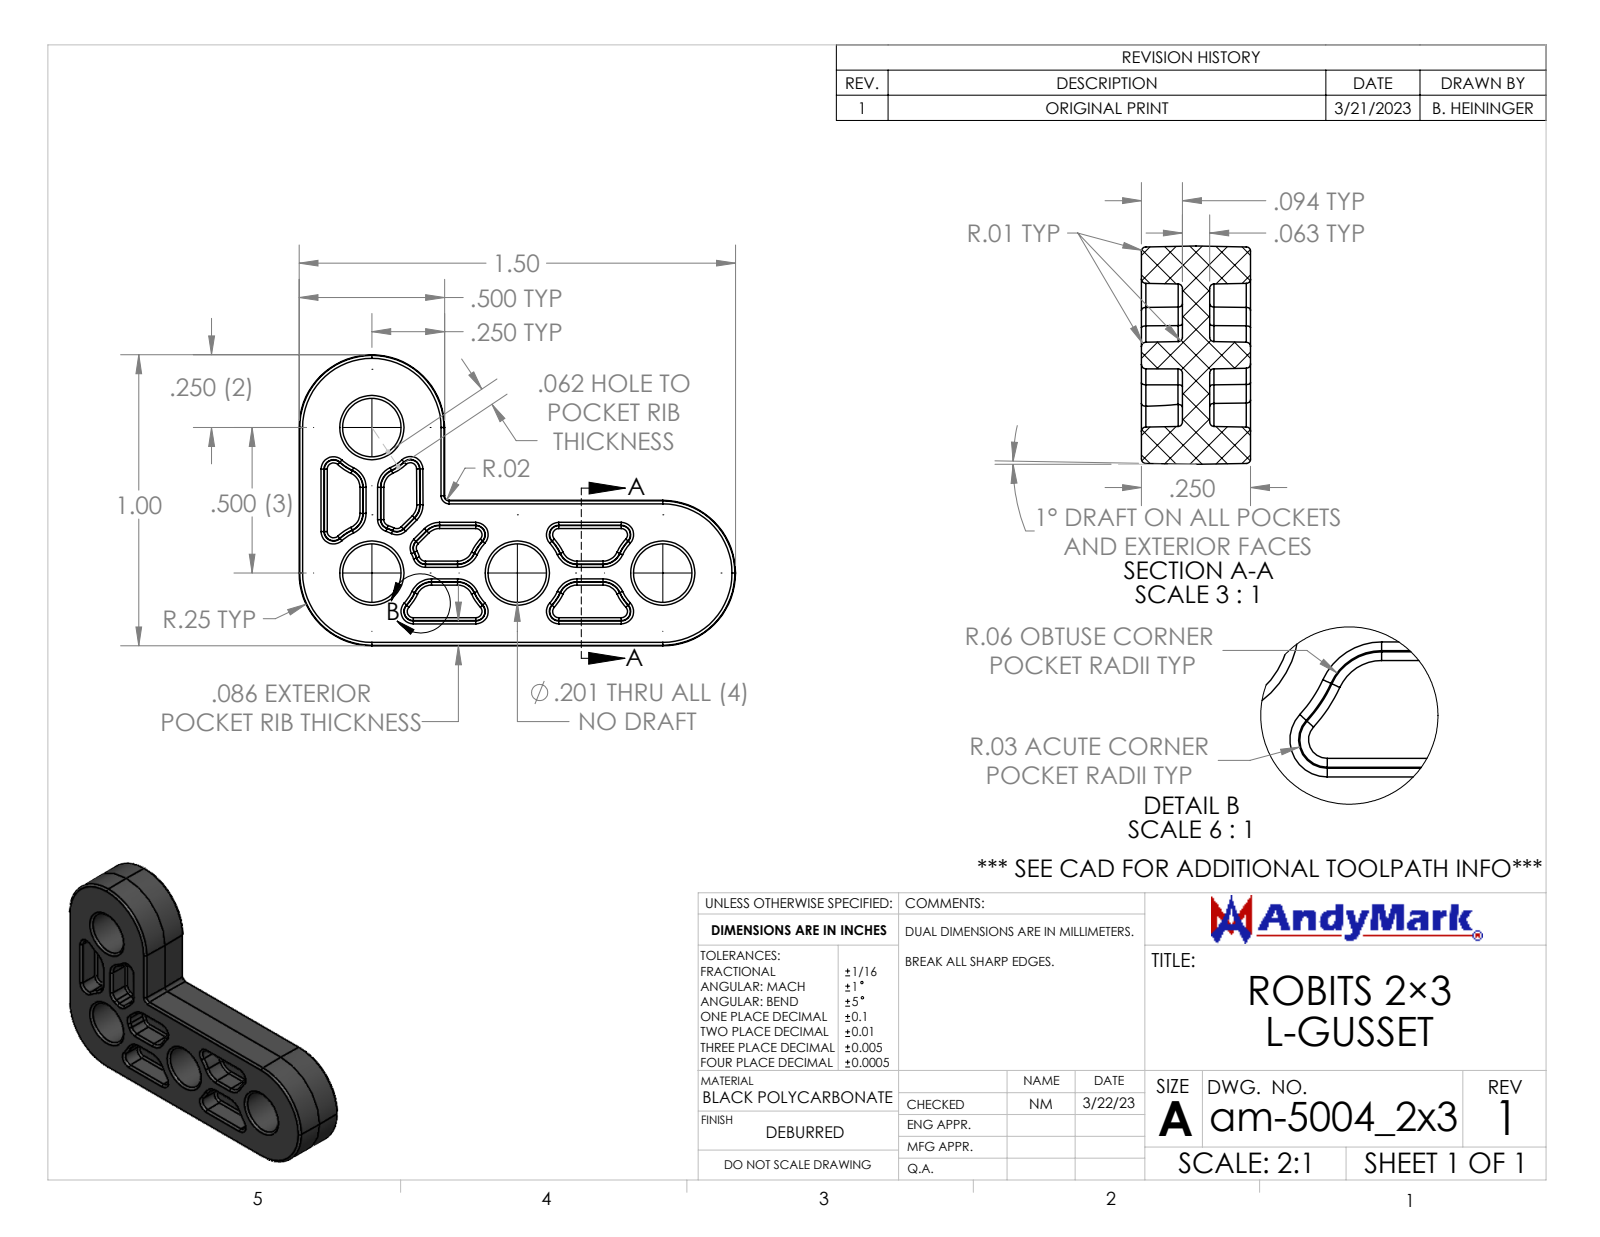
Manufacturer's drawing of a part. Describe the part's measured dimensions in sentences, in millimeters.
The part is named "am-5004_2x3 RoBits 2×3 L Gusset". Its 3-D file was written by "SolidWorks 2022 (AUTOMOTIVE_DESIGN)". It is 1 solid with 416 faces: 50 planar, 76 cylindrical and 290 other. Overall it measures 38.1 by 25.4 by 6.4 millimeters. Its volume is 2 740 cubic millimeters and its surface area 2 557 square millimeters. Round holes: 4 of diameter 5.1. Partial cylindrical surfaces (rounded edges, fillets, slot ends): 50 of radius 0.3, 2 of radius 1.6, 2 of radius 4.1. The main face-to-face distances are 6.4, 2.4, 4, 12.7, 10.5, 2.2, 1.6, 5.5, 7.2, 4.9. The hole center spacings are 12.7, 18, 25.4, 28.4.
